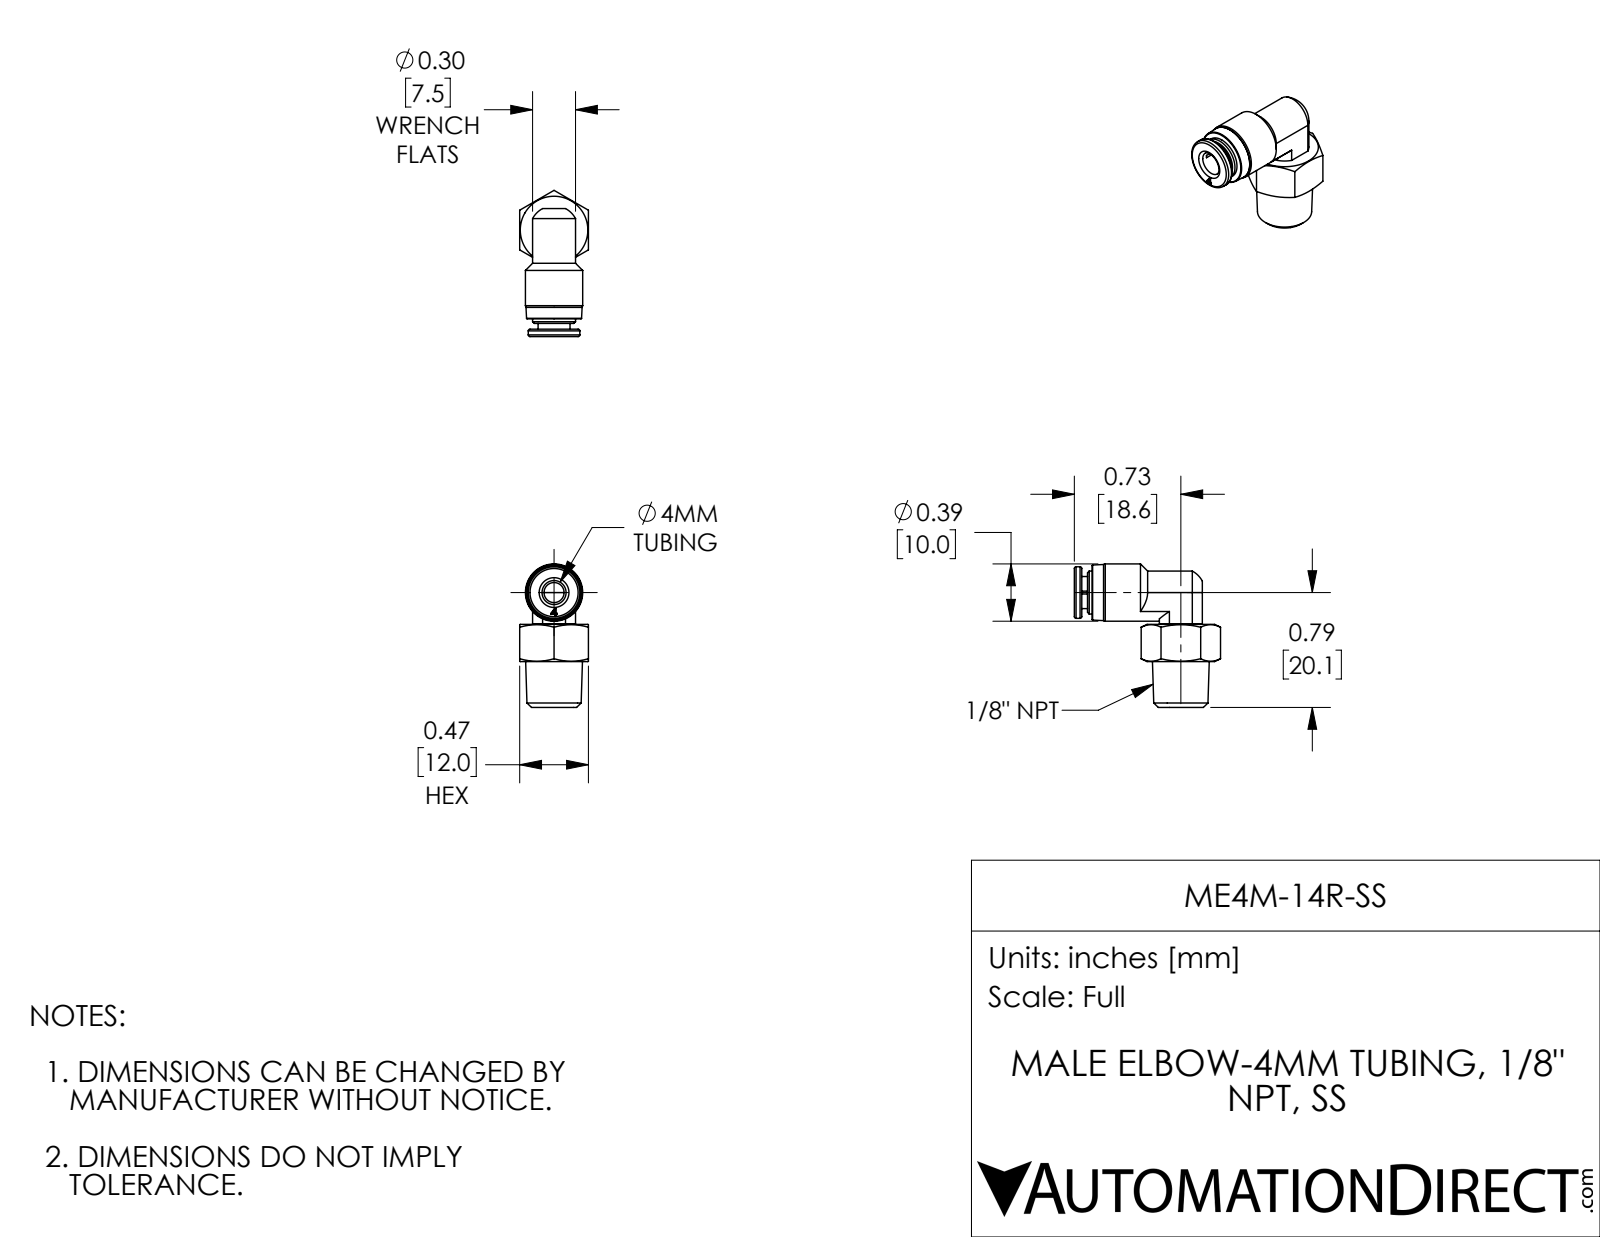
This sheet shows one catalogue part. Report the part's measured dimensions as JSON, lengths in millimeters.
{"part_name": "ME4M-14R-SS", "step_written_by": "SolidWorks 2017 (AUTOMOTIVE_DESIGN)", "units": "millimeters", "bodies": {"solids": 2, "faces": 108, "planar": 46, "cylindrical": 27, "other": 35}, "overall_size": [25.5, 25, 12], "volume_mm3": 2330, "surface_area_mm2": 2312, "round_holes": [[3.5, 2], [4, 1], [4.2, 1], [6, 1]], "round_bosses_or_shafts": [[10, 1], [9, 1], [7.5, 1], [6, 1], [5.6, 1]], "partial_cylinders_radius": [[4.2, 1]], "face_to_face_distances": [12, 9.8, 2.3, 7.5, 6.5, 1.3, 14.5, 8, 22.4, 21.1]}
